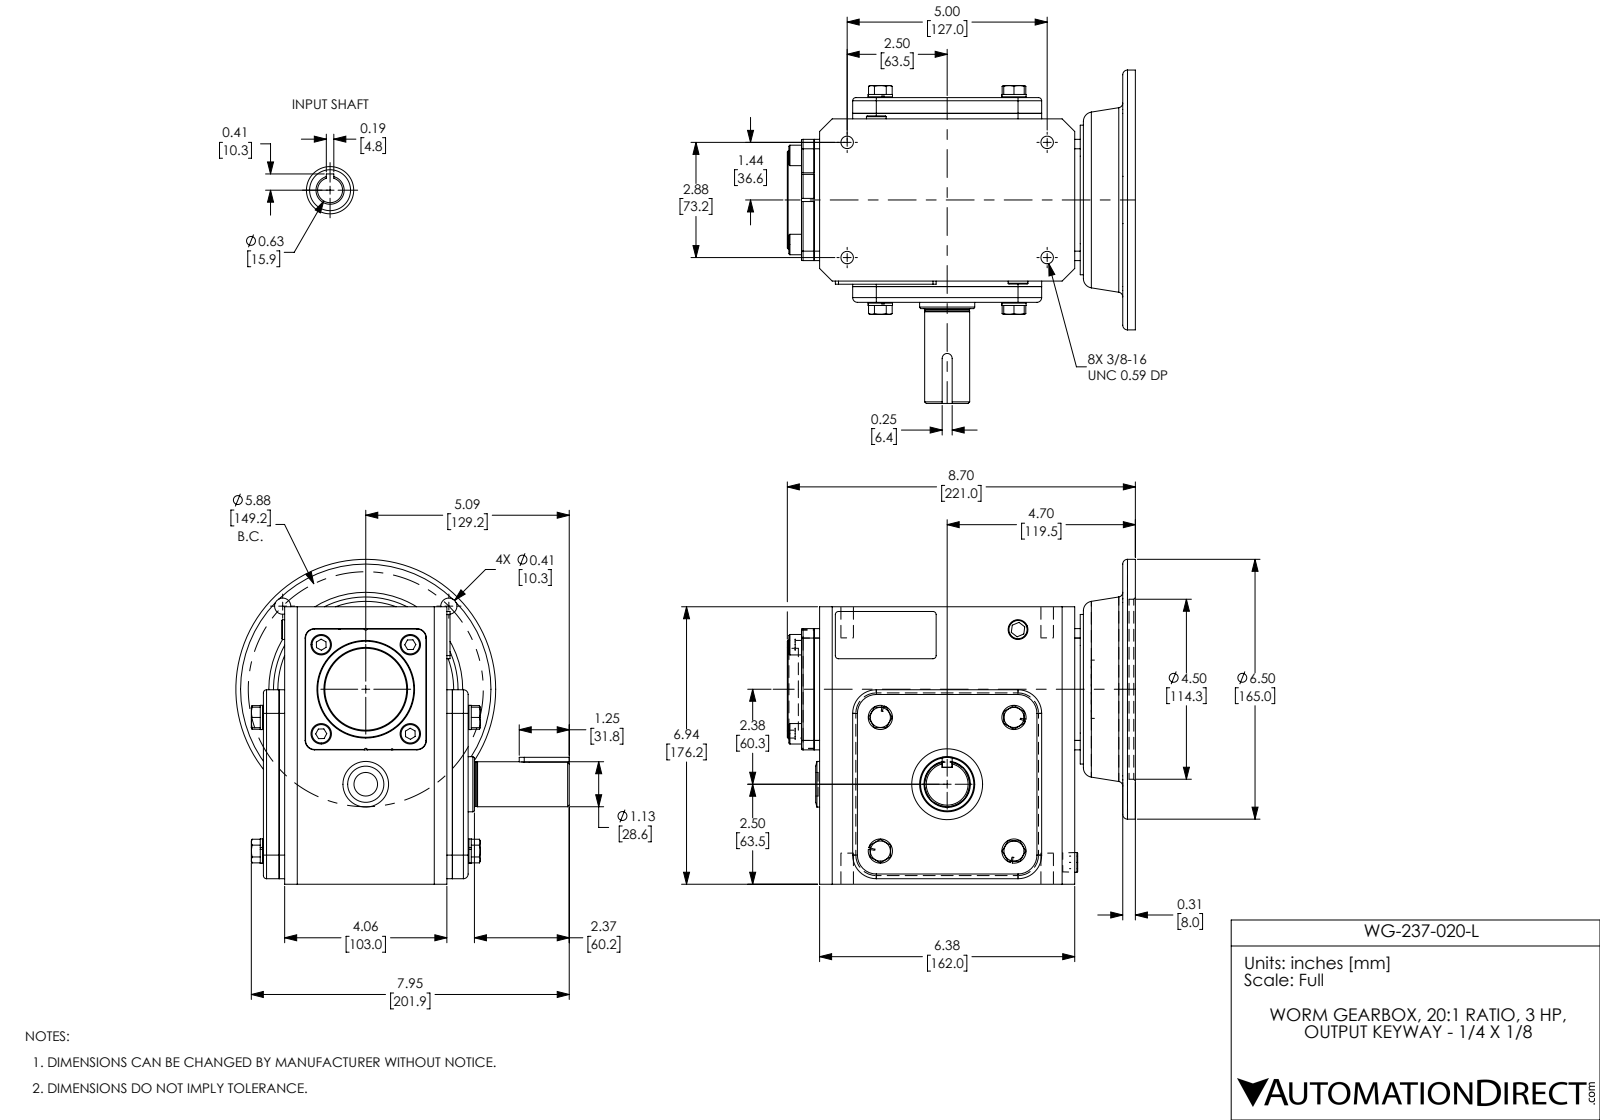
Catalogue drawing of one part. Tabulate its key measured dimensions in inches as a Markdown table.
| quantity | value |
| --- | --- |
| part name | WG-237-020-L |
| STEP written by | SolidWorks 2017 (AUTOMOTIVE_DESIGN) |
| units | inches |
| bodies | 37 solids, 542 faces (295 planar, 157 cylindrical, 90 other) |
| overall size | 8.701 × 8.335 × 8.123 |
| volume | 220.2 in³ |
| surface area | 513.5 in² |
| round holes (diameter × count) | 0.313 × 4, 0.406 × 4, 0.591 × 1, 0.625 × 1, 1.181 × 1, 1.378 × 1, 1.457 × 1, 1.772 × 1, 3.819 × 1, 4.5 × 1 |
| round bosses / shafts (diameter × count) | 0.606 × 4, 0.512 × 4, 6.496 × 1, 3.74 × 1, 2.441 × 1, 2.047 × 1, 1.142 × 1, 1.125 × 1 |
| partial cylindrical surfaces (radius × count) | 0.079 × 12, 0.236 × 6, 0.118 × 4, 0.591 × 4, 0.02 × 2, 0.039 × 2, 0.125 × 1 |
| main face-to-face distances | 0.138, 4.724, 0.394, 4.331, 0.531, 4.193, 4.587, 6.516, 6.937, 0.315 |
| hole center spacings | 2.937, 2.098, 2.88, 4.154, 4.154, 4.913, 5, 5.77 |
